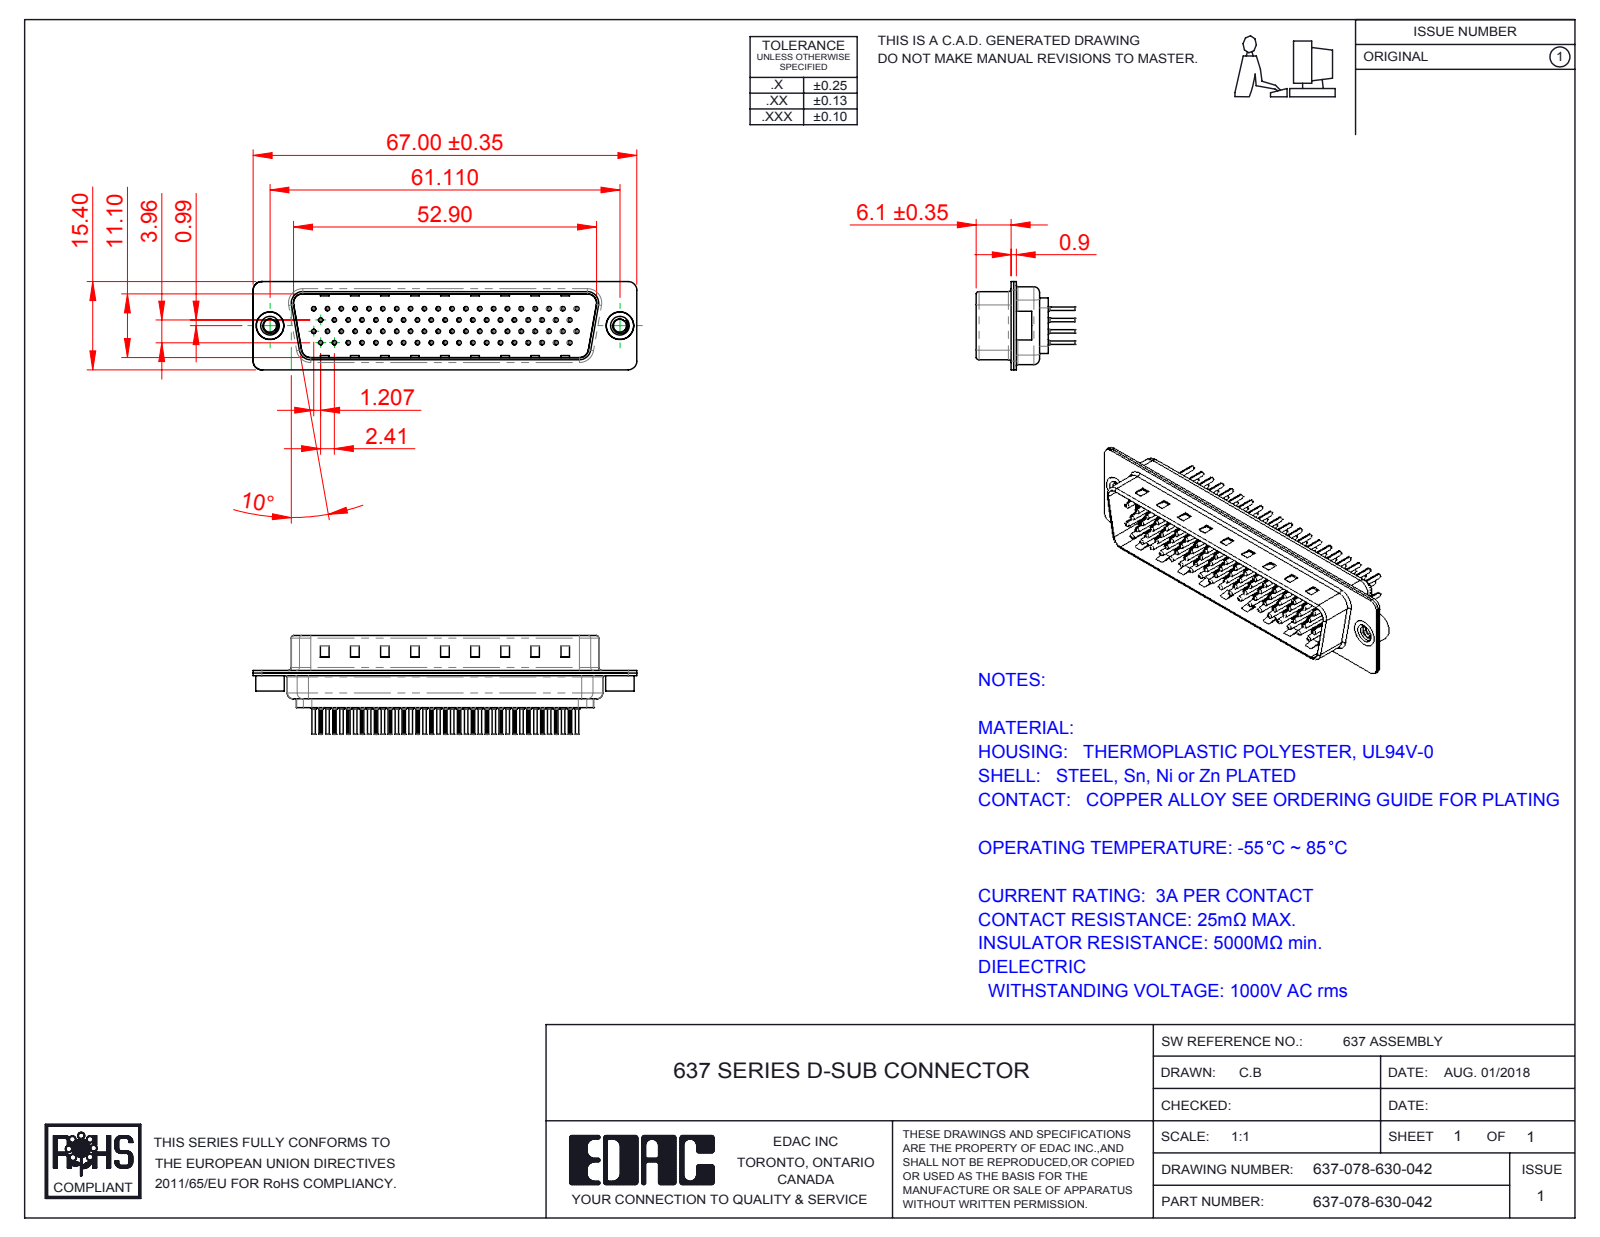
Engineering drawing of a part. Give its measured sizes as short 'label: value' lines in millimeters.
name: 637 Shell Rear_78 Contacts; 637 Contact Row 3_30; 637-078-630-042; 637 4-40 Threaded Rivet (+5 more)
written by: SolidWorks 2016 (CONFIG_CONTROL_DESIGN)
unit: mm
bodies: 83 solids, 8212 faces (2075 planar, 3027 cylindrical, 3110 other)
size: 67 × 17.25 × 15.4
volume: 4 336 mm³; area: 15 865 mm²
holes: 150× ⌀1.6, 78× ⌀0.2, 78× ⌀0.35, 78× ⌀1.1, 72× ⌀0.75, 72× ⌀2, 3× ⌀4, 2× ⌀2.26, 2× ⌀4.8
bosses: 78× ⌀2, 78× ⌀1.5, 78× ⌀0.75, 78× ⌀0.6, 2× ⌀5, 2× ⌀4.9, 1× ⌀4.8
rounds: 156× R0.1, 16× R1.5, 12× R2, 8× R0.5, 4× R0.25, 4× R0.55, 4× R0.7, 4× R0.95
face distances: 0.45, 0.4, 1.5, 1.95, 11.9, 11.5, 0.7, 11.1, 0.9, 0.8
hole spacings: 2.41, 7.24, 6.06, 9.65, 6.96, 8.46, 14.54, 16.89
